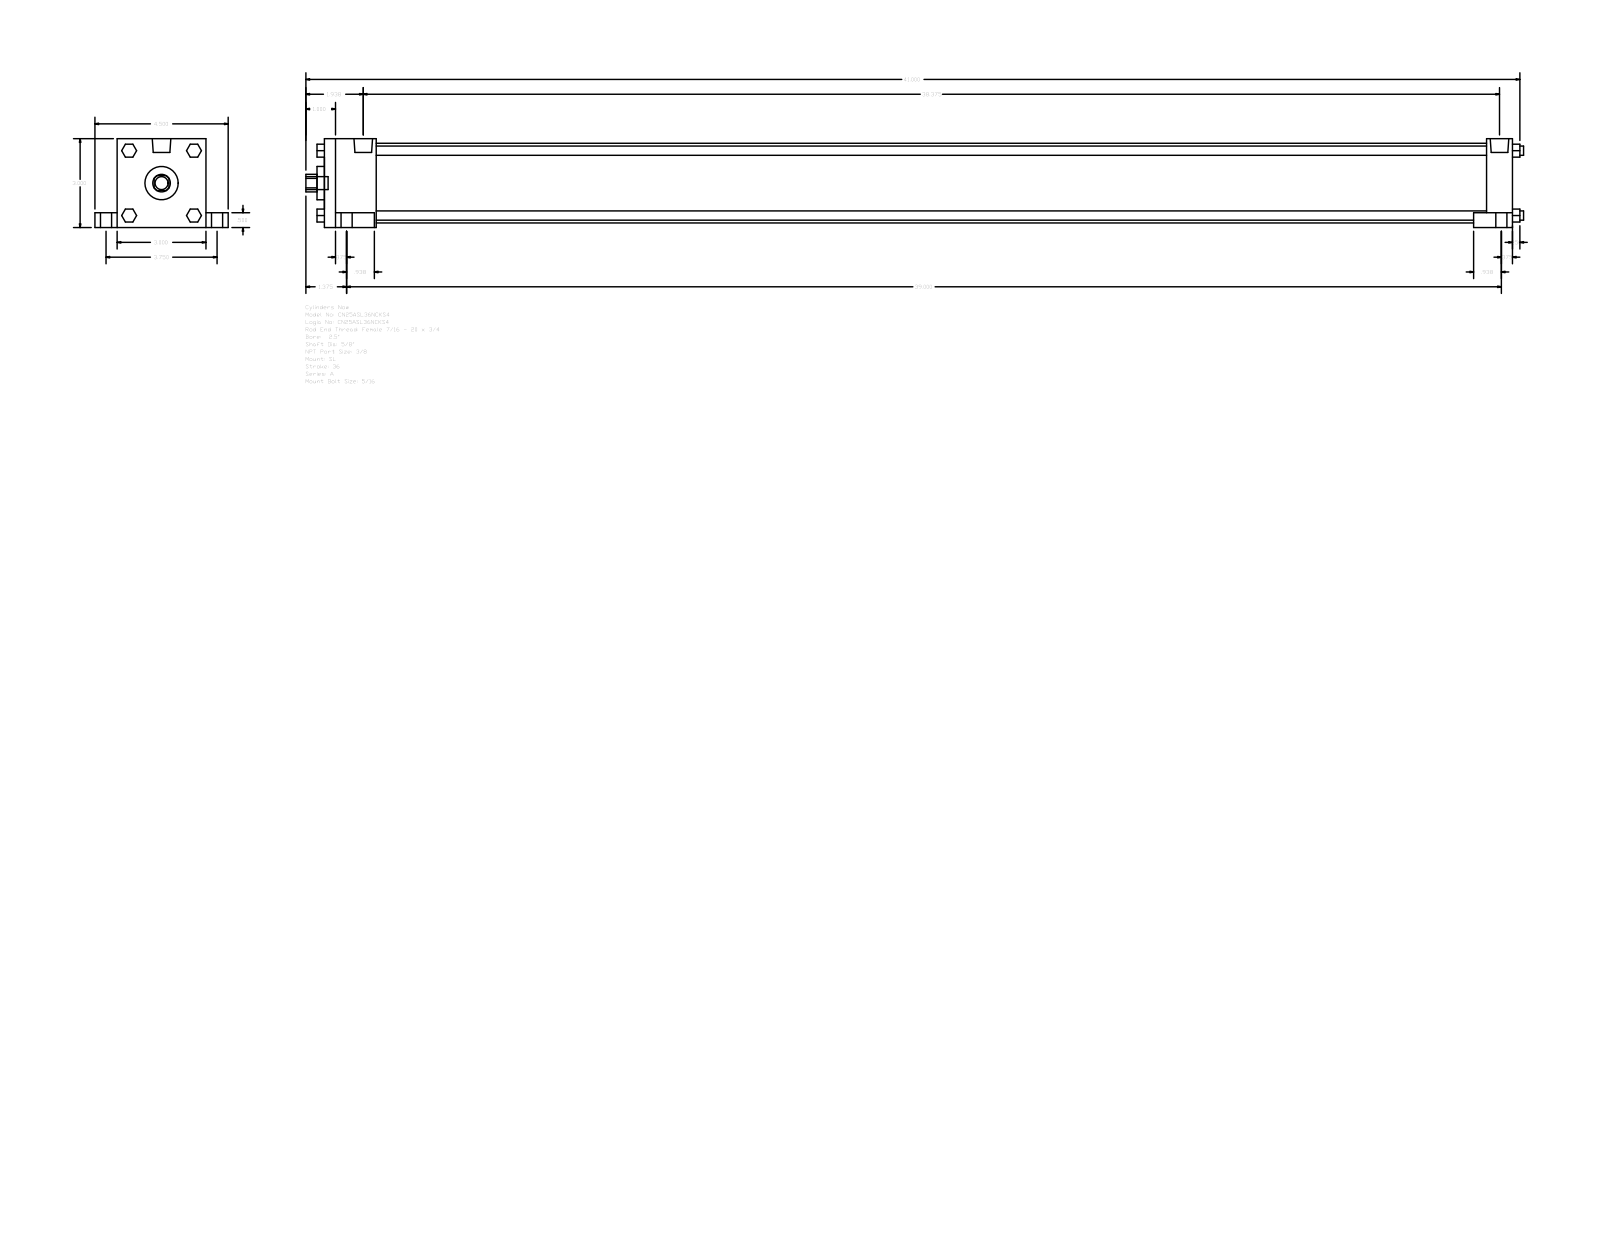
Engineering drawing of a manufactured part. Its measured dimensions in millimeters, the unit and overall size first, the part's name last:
Units: millimetres
Overall size (bounding box): 1044.58 × 114.3 × 76.2
Round holes (diameter × count): ⌀15.88 ×1, ⌀28.57 ×1, ⌀68.33 ×1
Round bosses / shafts (diameter × count): ⌀15.88 ×4, ⌀9.53 ×4, ⌀7.94 ×4, ⌀5.56 ×4, ⌀15.93 ×2, ⌀11.11 ×1
Partial cylindrical surfaces — rounded edges, fillets, slot ends (radius × count): R7.54 ×1
Main face-to-face distances: 76.2, 1019.17, 44.45, 22.22, 974.72, 996.95, 952.5, 12.7, 63.5, 19.05
Bodies: 0 solids, 148 faces (112 planar, 36 cylindrical, 0 other)
Part name (STEP PRODUCT): A_SL__0250_0.625
STEP written by: GSSL Pune (CONFIG_CONTROL_DESIGN)
